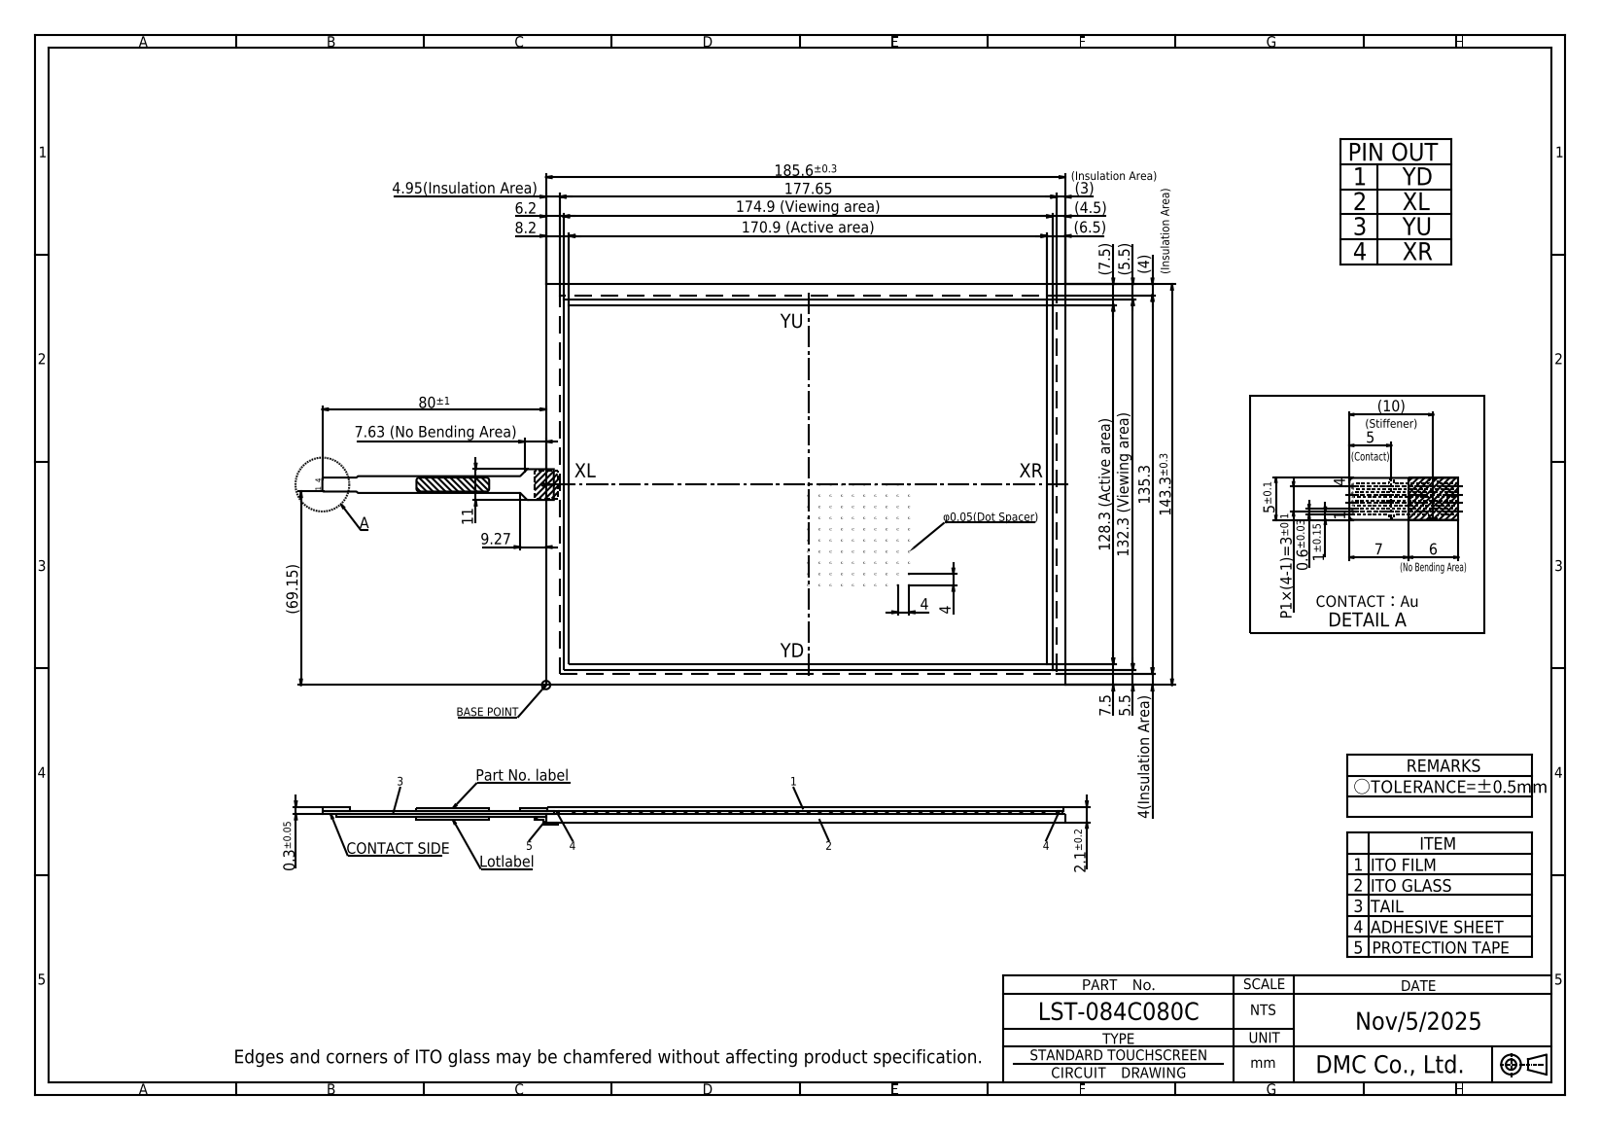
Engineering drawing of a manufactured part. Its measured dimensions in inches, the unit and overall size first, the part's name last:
Units: inches
Overall size (bounding box): 10.457 × 5.642 × 0.102
Partial cylindrical surfaces — rounded edges, fillets, slot ends (radius × count): R0.012 ×4, R0.02 ×2
Main face-to-face distances: 0.083, 0.079, 0.087, 0.091, 5.642, 7.307, 0.02, 0.024, 0.016, 0.102
Volume: 3.405 in³ · Surface area: 86.38 in²
Bodies: 2 solids, 52 faces (46 planar, 6 cylindrical, 0 other)
Part name (STEP PRODUCT): LST-084C080C (3Dデータ)
STEP written by: Autodesk Inventor 2020 (CONFIG_CONTROL_DESIGN)
